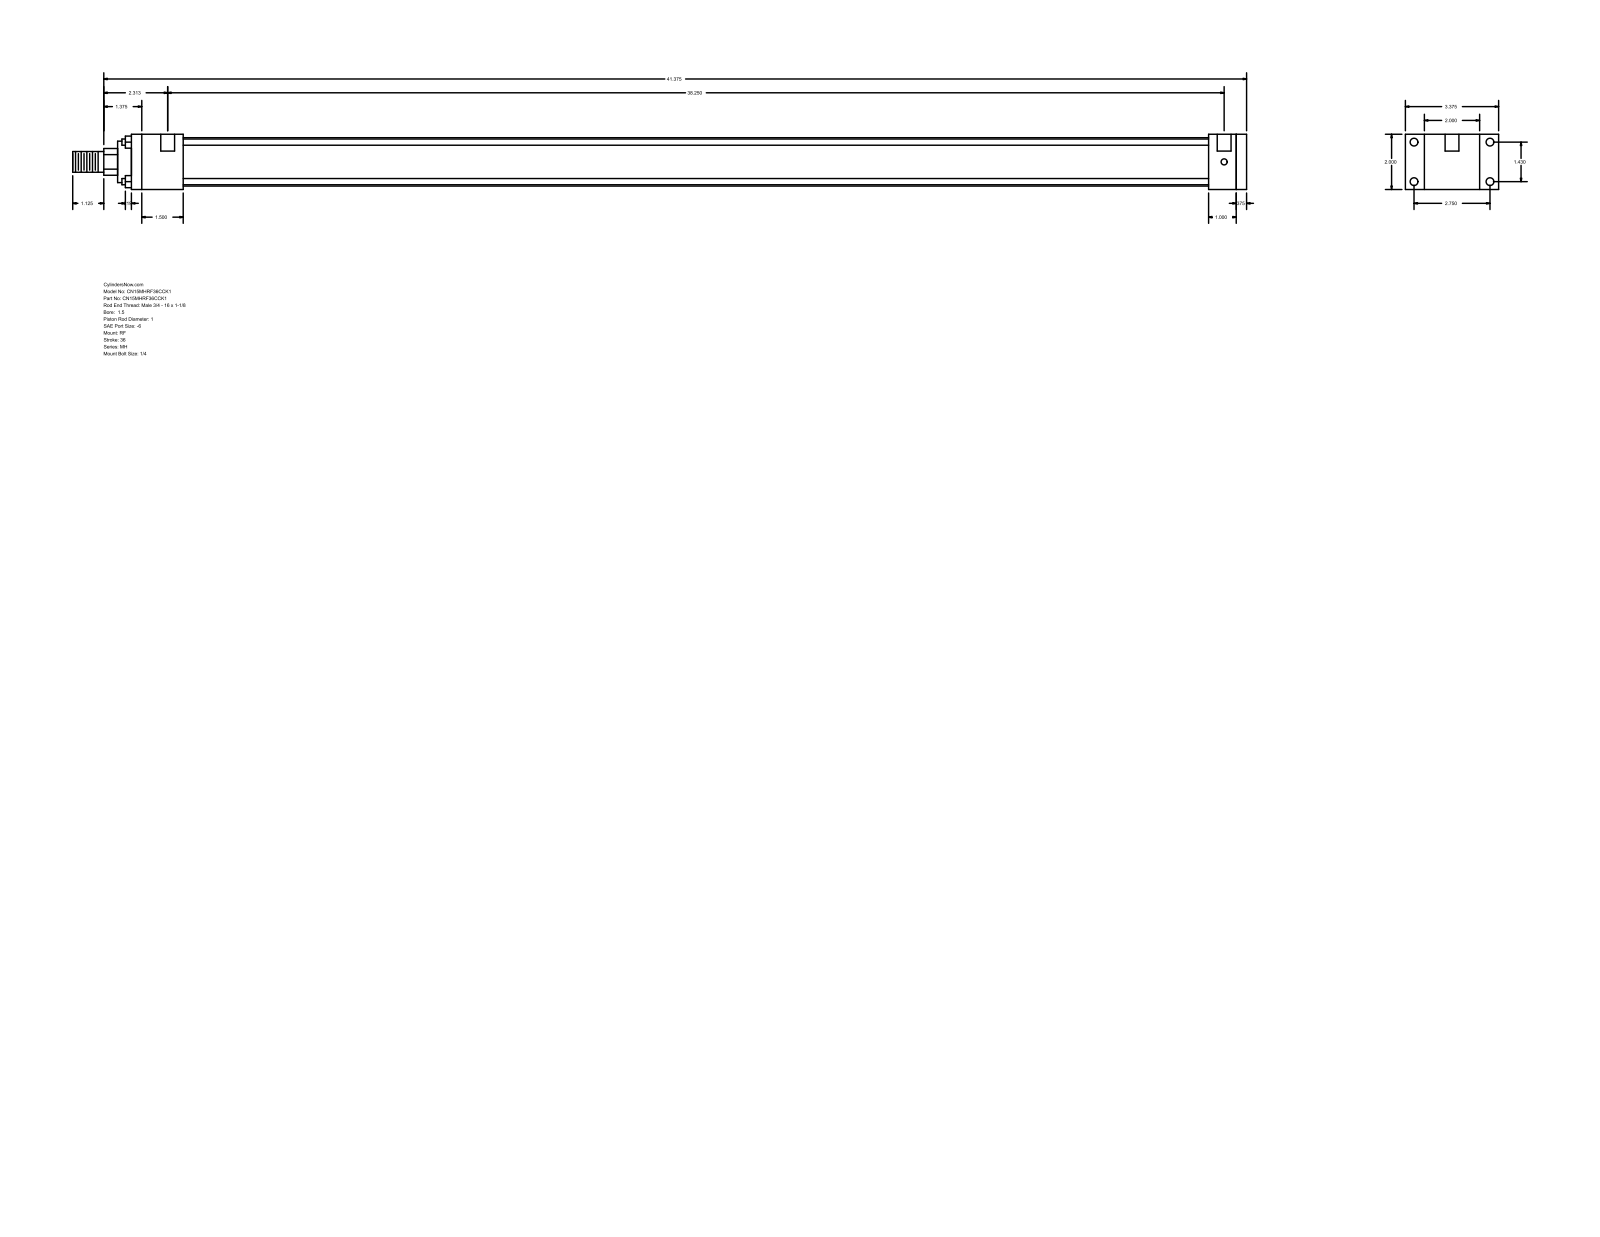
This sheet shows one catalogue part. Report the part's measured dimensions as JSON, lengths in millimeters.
{"part_name": "MH_RF__0150_1", "step_written_by": "GSSL Pune (CONFIG_CONTROL_DESIGN)", "units": "millimeters", "bodies": {"solids": 0, "faces": 92, "planar": 64, "cylindrical": 28, "other": 0}, "overall_size": [1079.5, 85.72, 50.8], "round_holes": [[5.56, 4], [7.14, 4], [12.7, 2]], "round_bosses_or_shafts": [[5.71, 4], [44.45, 1], [38.1, 1], [25.4, 1], [19.05, 1]], "partial_cylinders_radius": [[12.29, 1]], "face_to_face_distances": [50.8, 9.52, 1016, 25.4, 1025.52, 17.46, 68.26, 990.6, 34.92, 47.63], "hole_center_spacings": [36.32, 69.84, 78.72, 974.73, 3.18, 971.55]}
